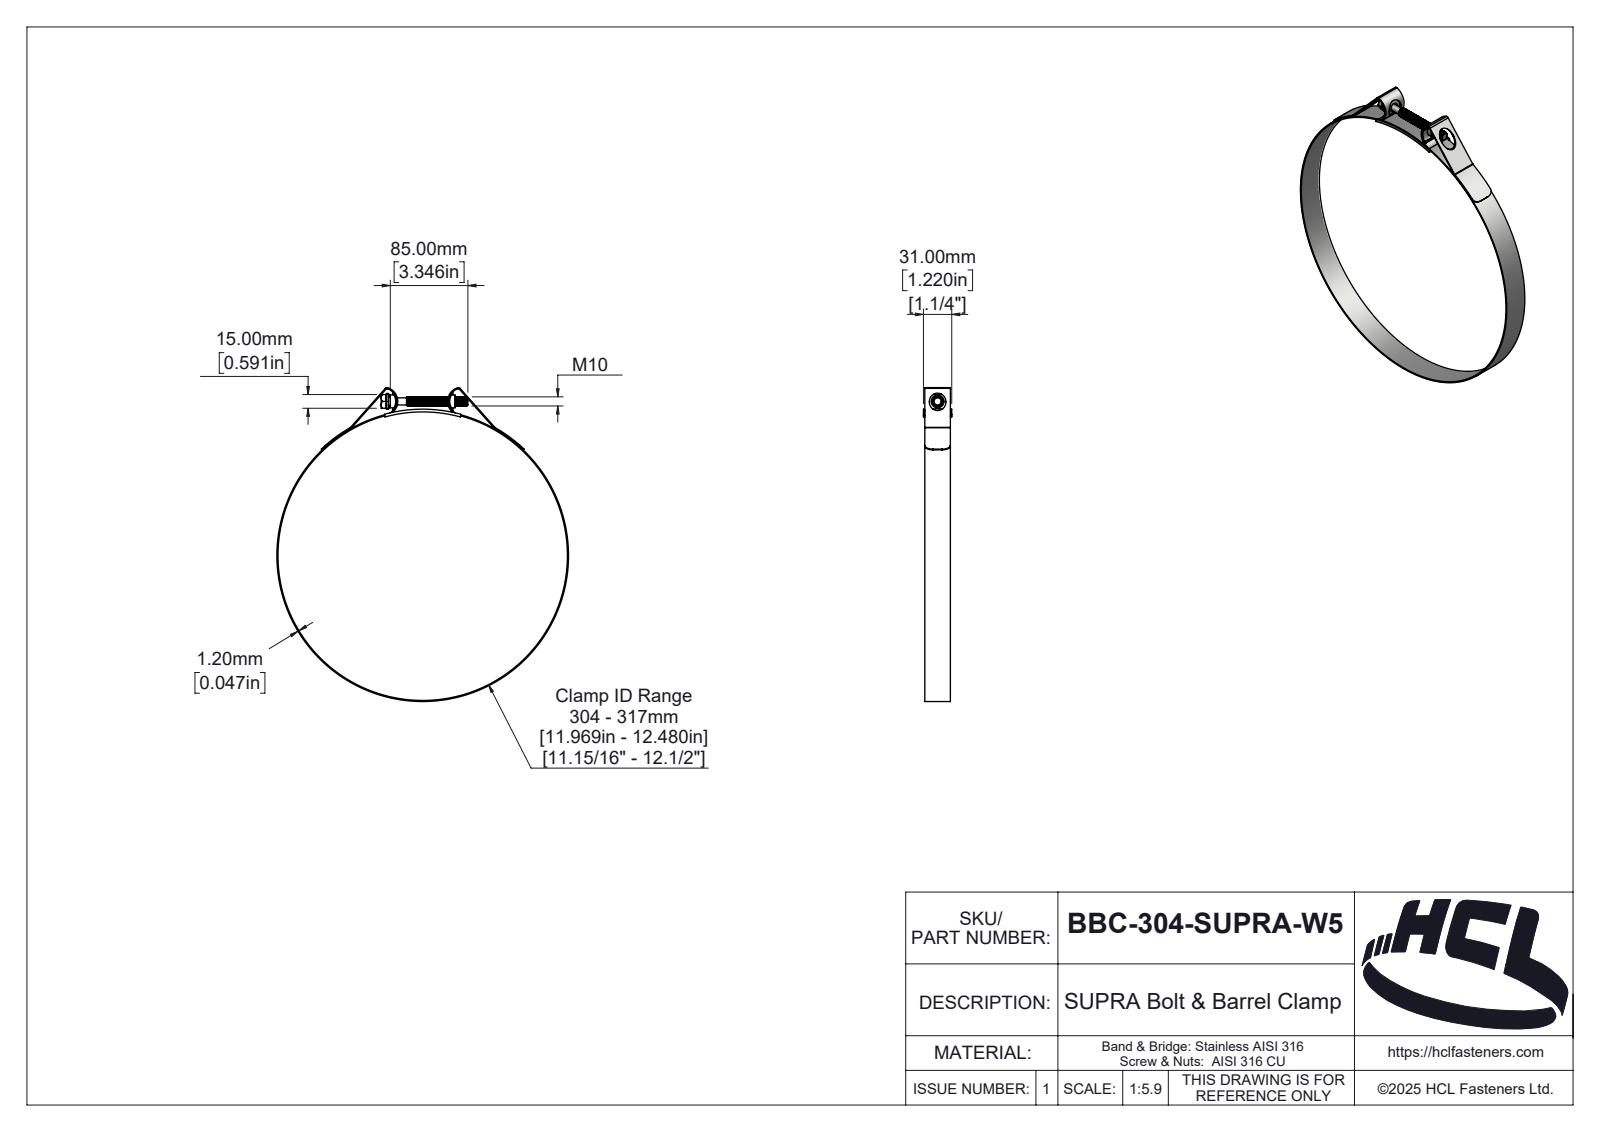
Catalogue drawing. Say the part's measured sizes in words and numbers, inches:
The part is named "BBC-304-SUPRA-W5". Its 3-D file was written by "SolidWorks 2025 (AUTOMOTIVE_DESIGN)". It is 5 solids with 379 faces: 50 planar, 243 cylindrical and 86 other. Overall it measures 13.528 by 12.575 by 1.22 inches. Its volume is 3.14 cubic inches and its surface area 126.2 square inches. Round holes: 1 of diameter 12.48. Round bosses or shafts: 1 of diameter 12.575, 1 of diameter 0.682, 1 of diameter 0.551, 1 of diameter 0.394, 1 of diameter 0.307. Partial cylindrical surfaces (rounded edges, fillets, slot ends): 4 of radius 0.039, 2 of radius 0.051, 2 of radius 0.079, 2 of radius 0.098, 2 of radius 0.126, 2 of radius 0.354, 2 of radius 0.527, 2 of radius 0.567. The main face-to-face distances are 0.047, 1.102, 0.059, 1.161, 1.173, 1.114, 1.22, 1.126, 0.591, 0.098.
